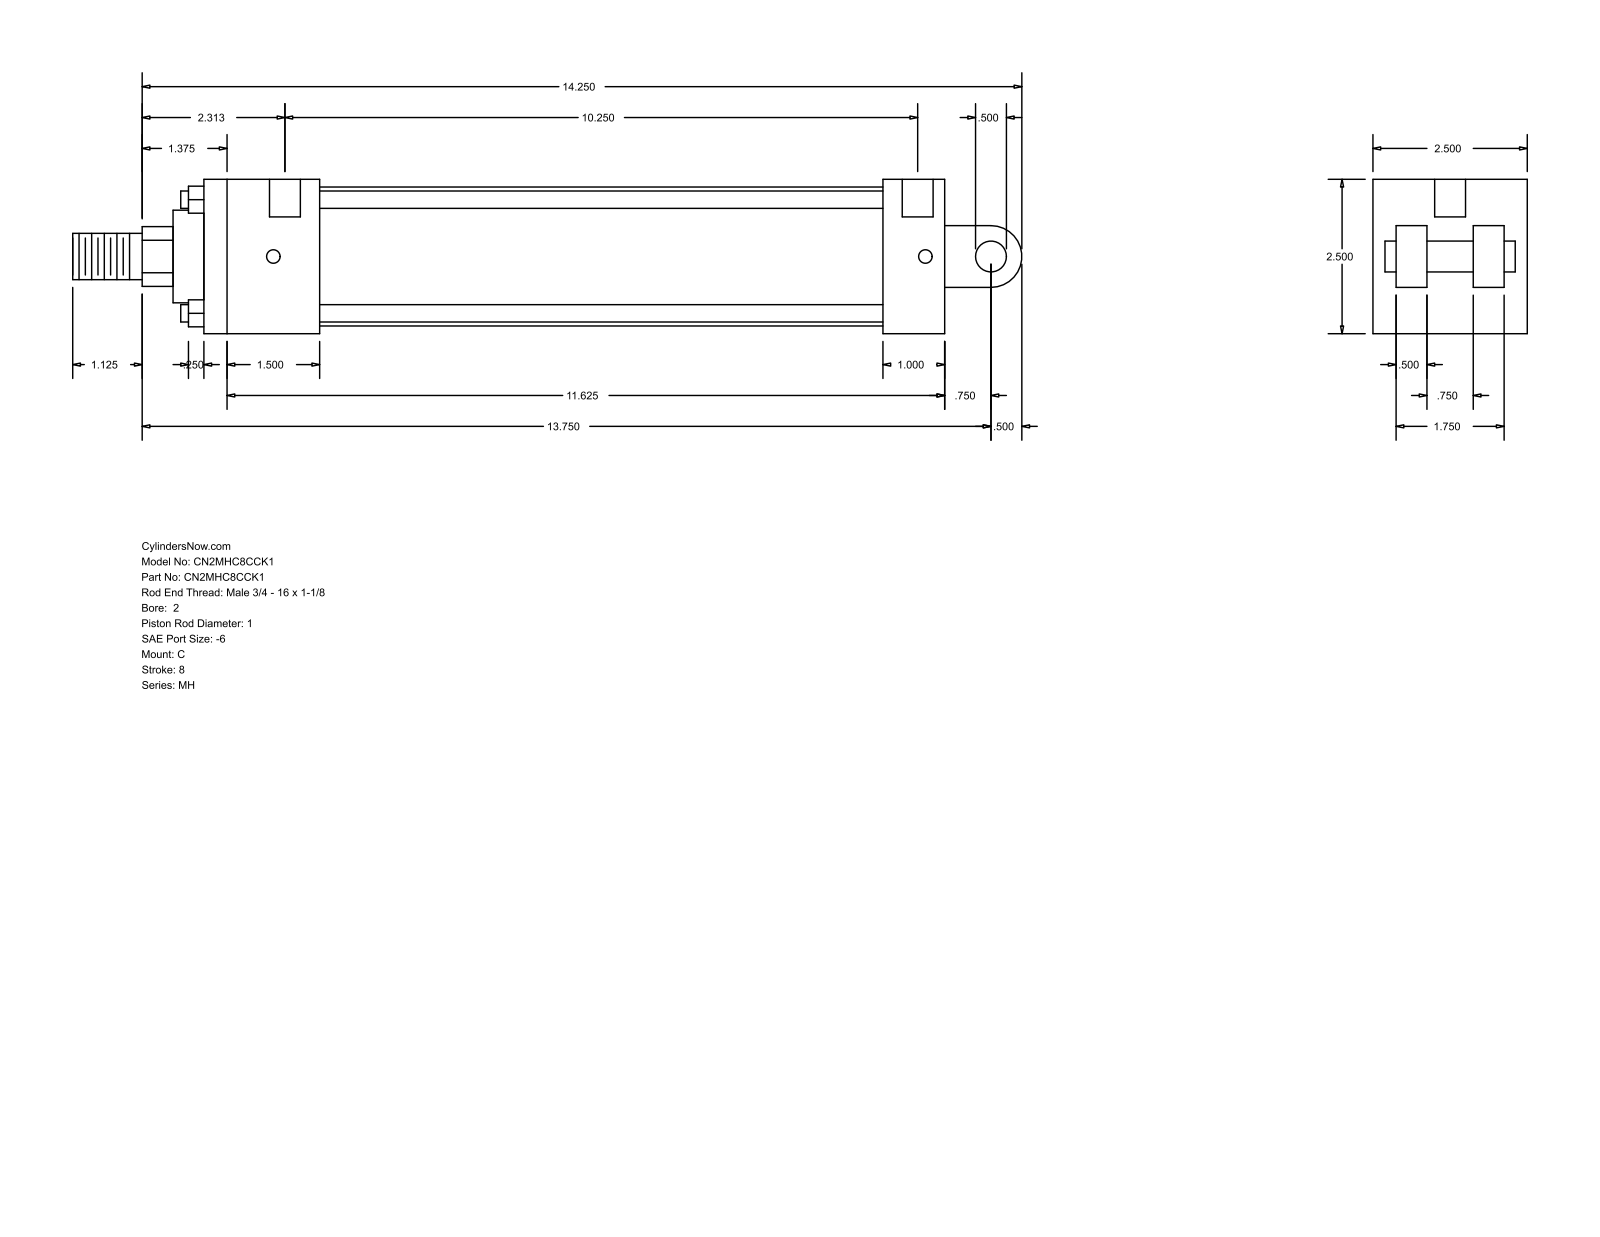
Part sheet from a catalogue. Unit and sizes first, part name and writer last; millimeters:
Units: millimetres
Overall size (bounding box): 390.52 × 63.5 × 63.5
Round holes (diameter × count): ⌀5.56 ×4, ⌀12.7 ×2
Round bosses / shafts (diameter × count): ⌀7.14 ×4, ⌀57.15 ×1, ⌀38.1 ×1, ⌀25.4 ×1, ⌀19.05 ×1, ⌀12.7 ×1
Partial cylindrical surfaces — rounded edges, fillets, slot ends (radius × count): R12.29 ×1, R12.7 ×1
Main face-to-face distances: 63.5, 304.8, 12.7, 25.4, 47.63, 53.98, 9.52, 279.4, 231.77, 257.17
Hole centre spacings: 268.28, 3.17, 4.76, 260.35, 263.52, 265.11
Bodies: 0 solids, 99 faces (70 planar, 29 cylindrical, 0 other)
Part name (STEP PRODUCT): MH_C__0200_1
STEP written by: GSSL Pune (CONFIG_CONTROL_DESIGN)
